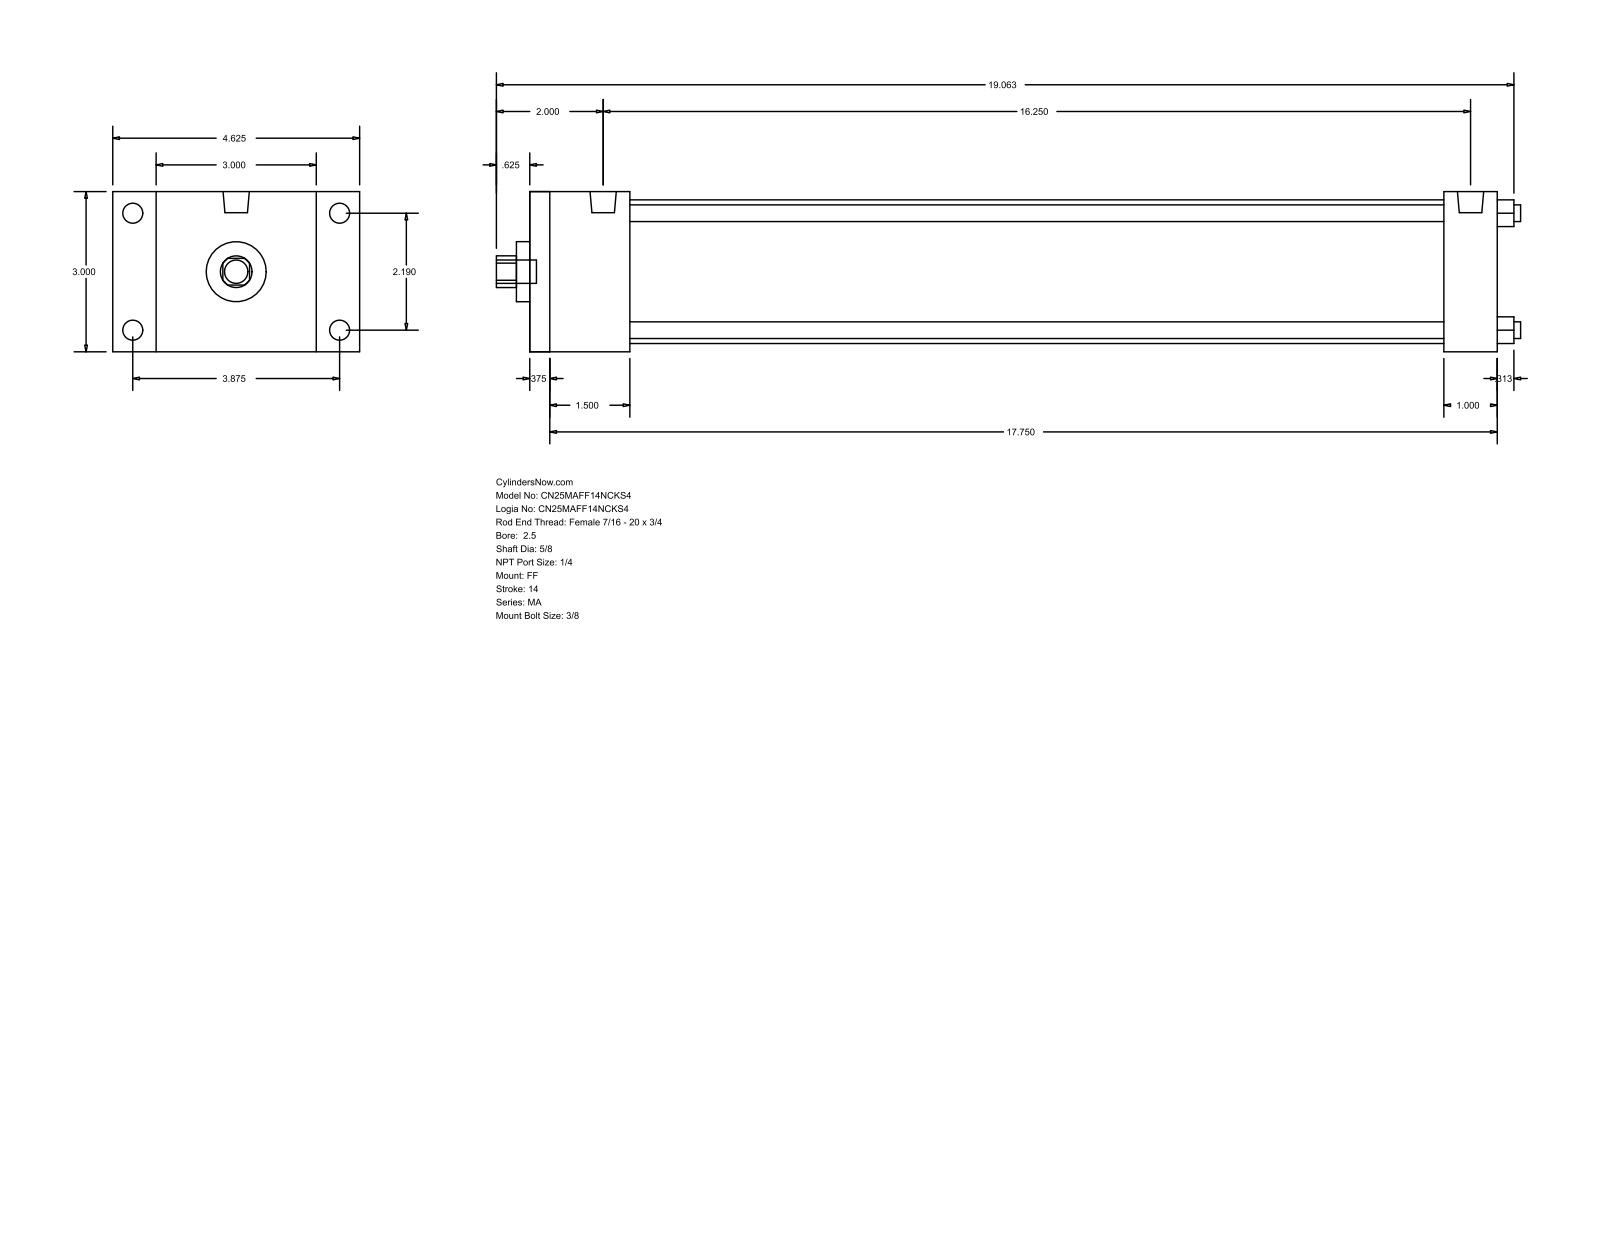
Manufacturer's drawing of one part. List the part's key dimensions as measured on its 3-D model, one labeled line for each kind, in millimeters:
Part name (STEP PRODUCT): MA_FF__0250_0.625
STEP written by: GSSL Pune (CONFIG_CONTROL_DESIGN)
Units: millimetres
Bodies: 0 solids, 92 faces (64 planar, 28 cylindrical, 0 other)
Overall size (bounding box): 487.36 × 117.47 × 76.2
Round holes (diameter × count): ⌀7.94 ×4, ⌀15.88 ×1, ⌀28.57 ×1, ⌀68.33 ×1
Round bosses / shafts (diameter × count): ⌀9.53 ×4, ⌀7.94 ×4, ⌀12.49 ×2, ⌀11.11 ×1
Partial cylindrical surfaces — rounded edges, fillets, slot ends (radius × count): R7.54 ×1
Main face-to-face distances: 76.2, 460.37, 9.52, 450.85, 25.4, 47.62, 434.97, 38.1, 425.45, 387.35
Hole centre spacings: 39.33, 55.62, 78.66
